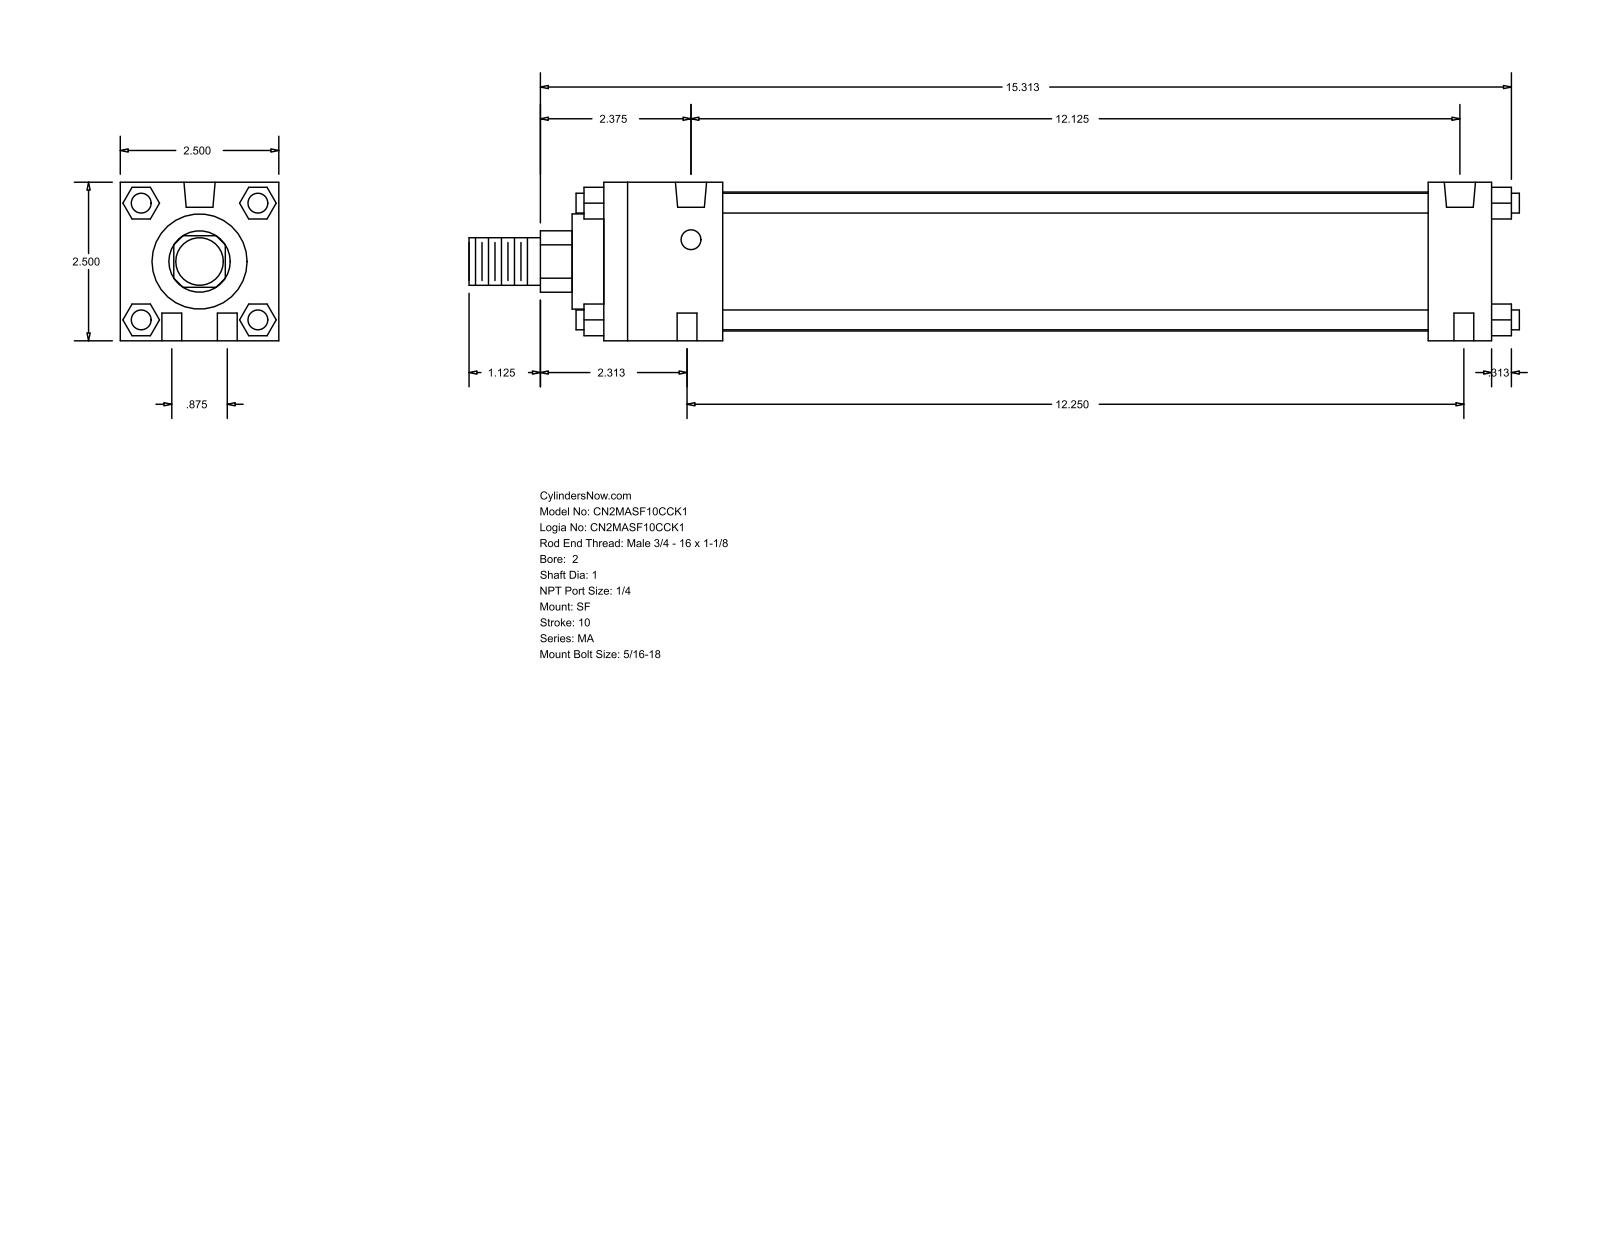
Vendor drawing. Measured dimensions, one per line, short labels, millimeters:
name: MA_SF__0200_1
written by: GSSL Pune (CONFIG_CONTROL_DESIGN)
unit: mm
bodies: 0 solids, 124 faces (94 planar, 30 cylindrical, 0 other)
size: 420.69 × 63.5 × 63.5
holes: 6× ⌀7.94, 2× ⌀12.49
bosses: 4× ⌀7.94, 1× ⌀55.63, 1× ⌀38.1, 1× ⌀25.4, 1× ⌀19.05
rounds: 1× R12.29
face distances: 63.5, 355.6, 12.7, 25.4, 330.2, 47.63, 282.57, 307.97, 40.47, 23.37
hole spacings: 11.22, 309.76, 22.22, 307.97, 311.15, 311.94
